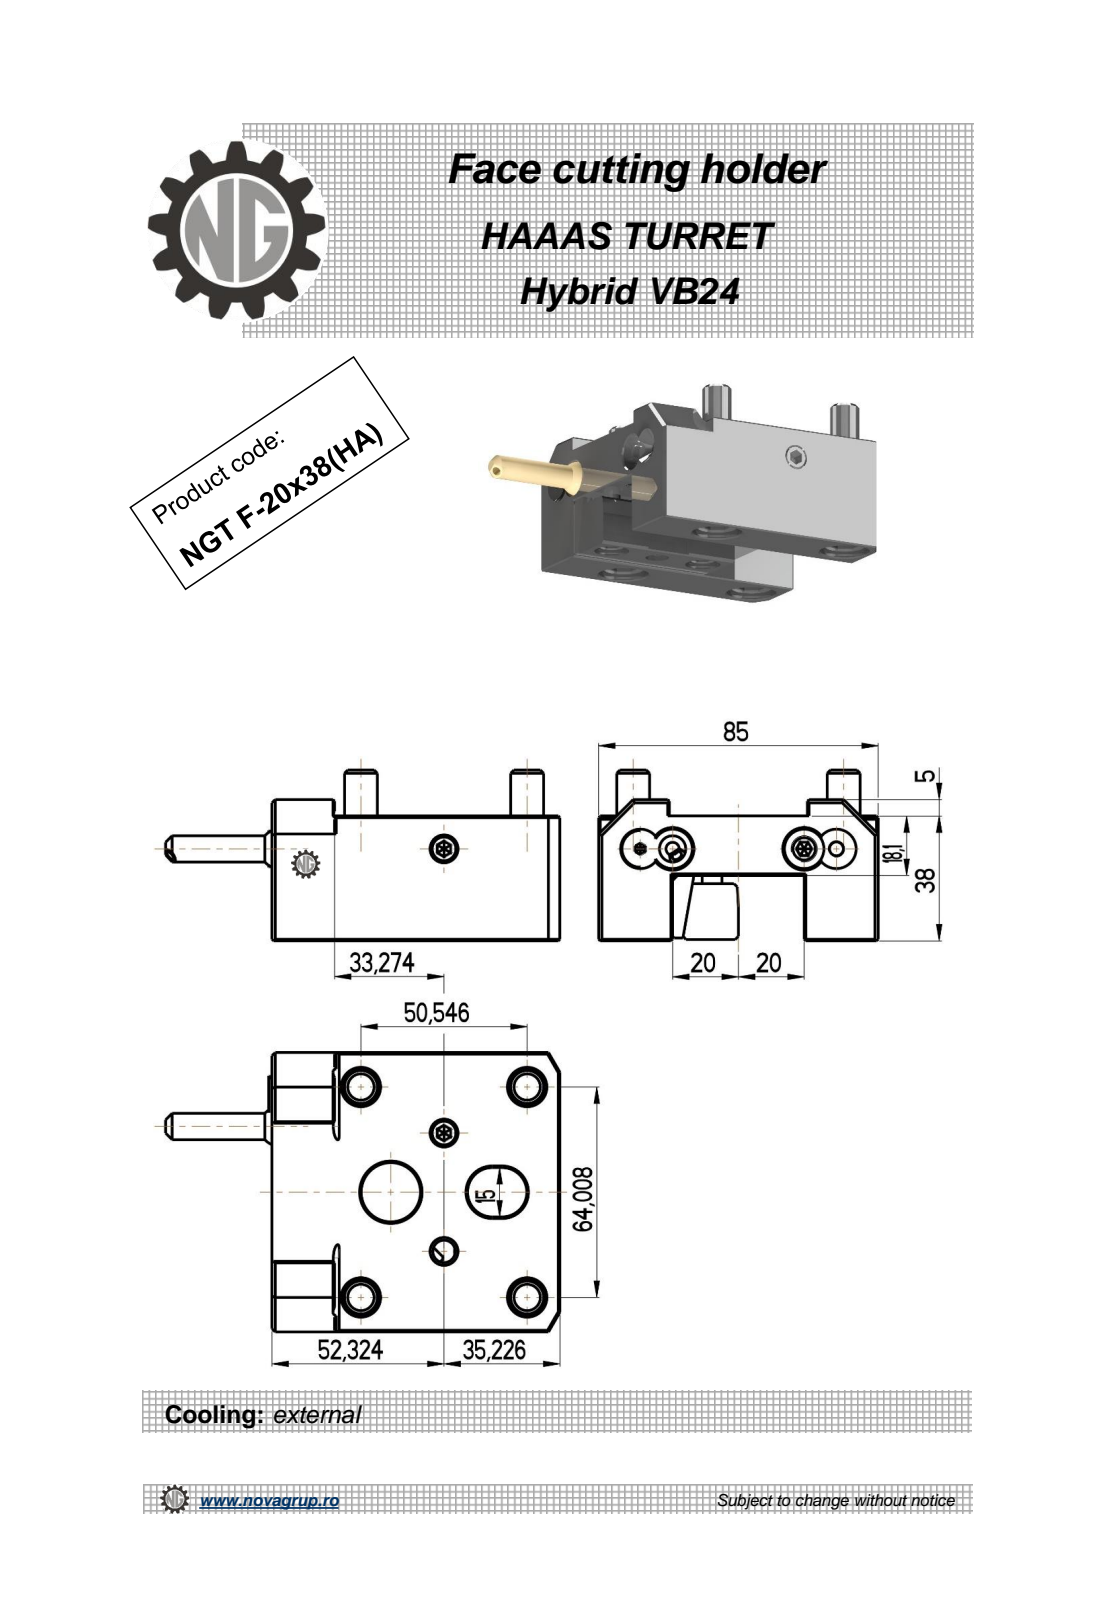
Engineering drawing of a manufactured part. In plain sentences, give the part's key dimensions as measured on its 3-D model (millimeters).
The part is named "NGT_F_20_38_HA". Its 3-D file was written by "PRO/ENGINEER BY PARAMETRIC TECHNOLOGY CORPORATION, 2010280 (CONFIG_CONTROL_DESIGN)". It is 1 solid with 198 faces: 120 planar, 41 cylindrical and 37 other. Overall it measures 119.89 by 85 by 52 millimeters. Its volume is 234 964 cubic millimeters and its surface area 35 989 square millimeters. Round holes: 1 of diameter 3, 1 of diameter 5, 1 of diameter 6.8, 1 of diameter 18. Round bosses or shafts: 4 of diameter 10, 3 of diameter 6, 1 of diameter 11.2, 1 of diameter 8. Partial cylindrical surfaces (rounded edges, fillets, slot ends): 6 of radius 0.22, 6 of radius 0.41, 2 of radius 7.5, 1 of radius 1. The main face-to-face distances are 38, 18.1, 19.9, 85, 22.5, 62.5, 87.55, 5, 40, 37.58. The hole center spacings are 24.2.
